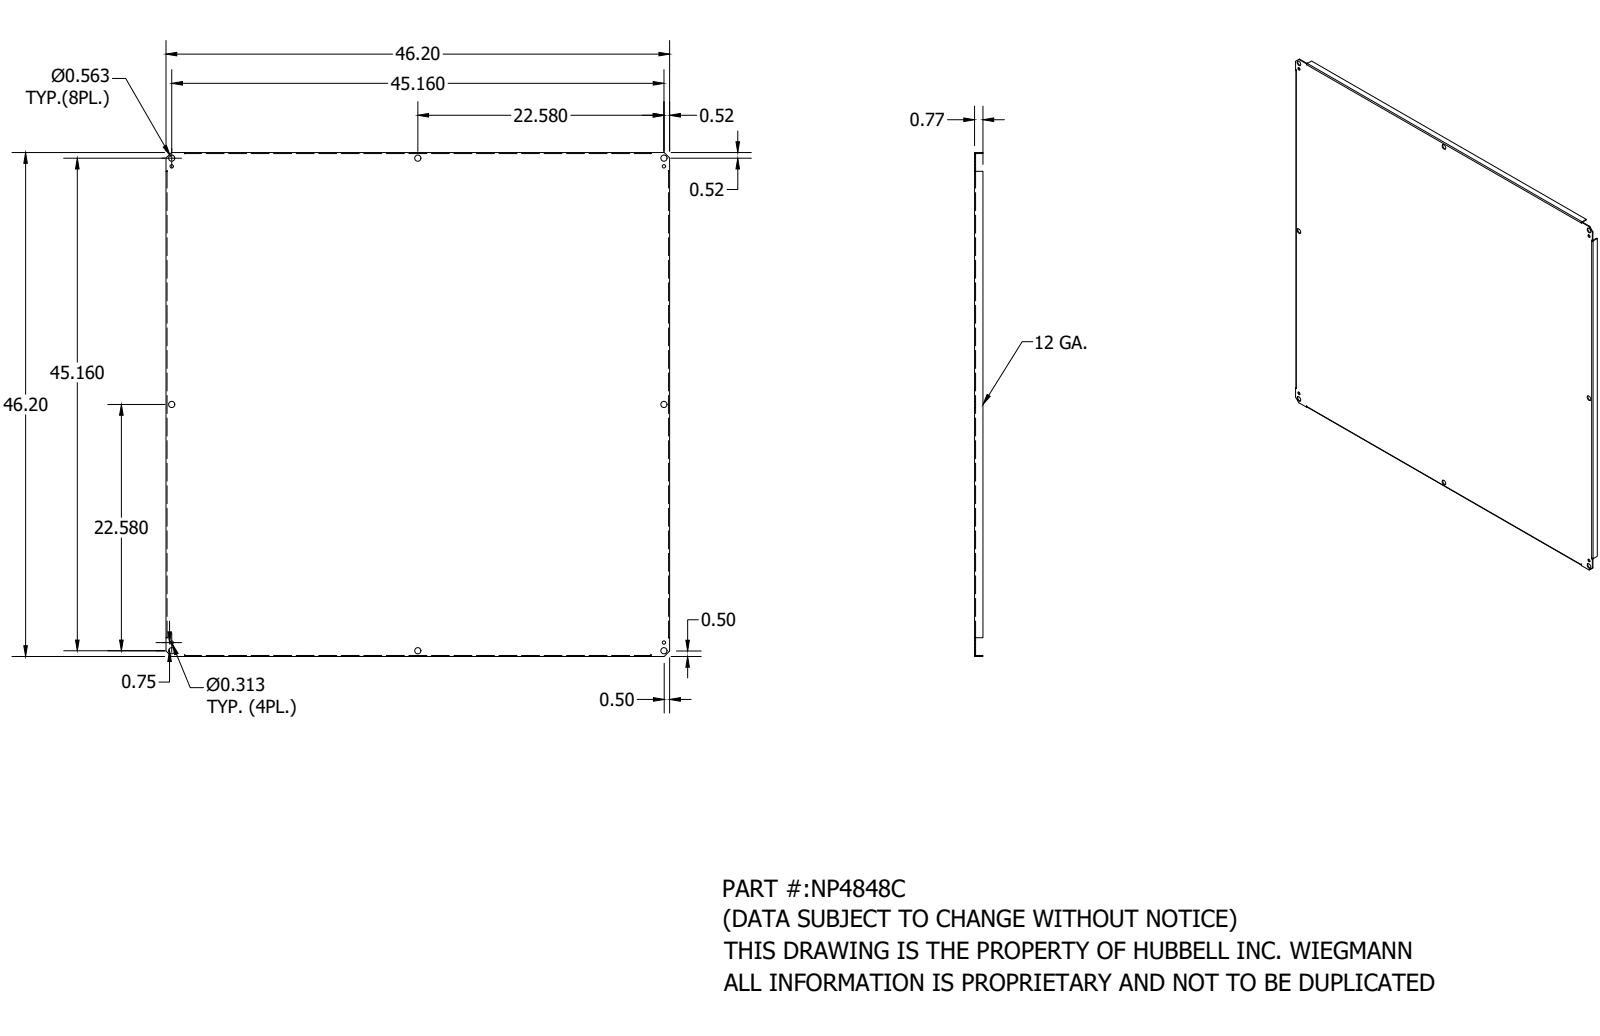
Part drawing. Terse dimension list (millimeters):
name: NP4848C
written by: Autodesk Inventor 2018 (AUTOMOTIVE_DESIGN)
unit: mm
bodies: 1 solid, 70 faces (50 planar, 20 cylindrical, 0 other)
size: 1173.5 × 1173.5 × 19.7
volume: 3 446 000 mm³; area: 2 907 000 mm²
holes: 8× ⌀14.3, 4× ⌀8
rounds: 4× R0.4, 4× R2.8
face distances: 2.4, 1171.1, 1173.5, 1168.7, 17.3, 19.7, 43.6, 1129.8, 41.2, 1127.5
hole spacings: 573.5, 1147.1, 1282.4, 19.1, 554.5, 573.9, 811.1, 1128
